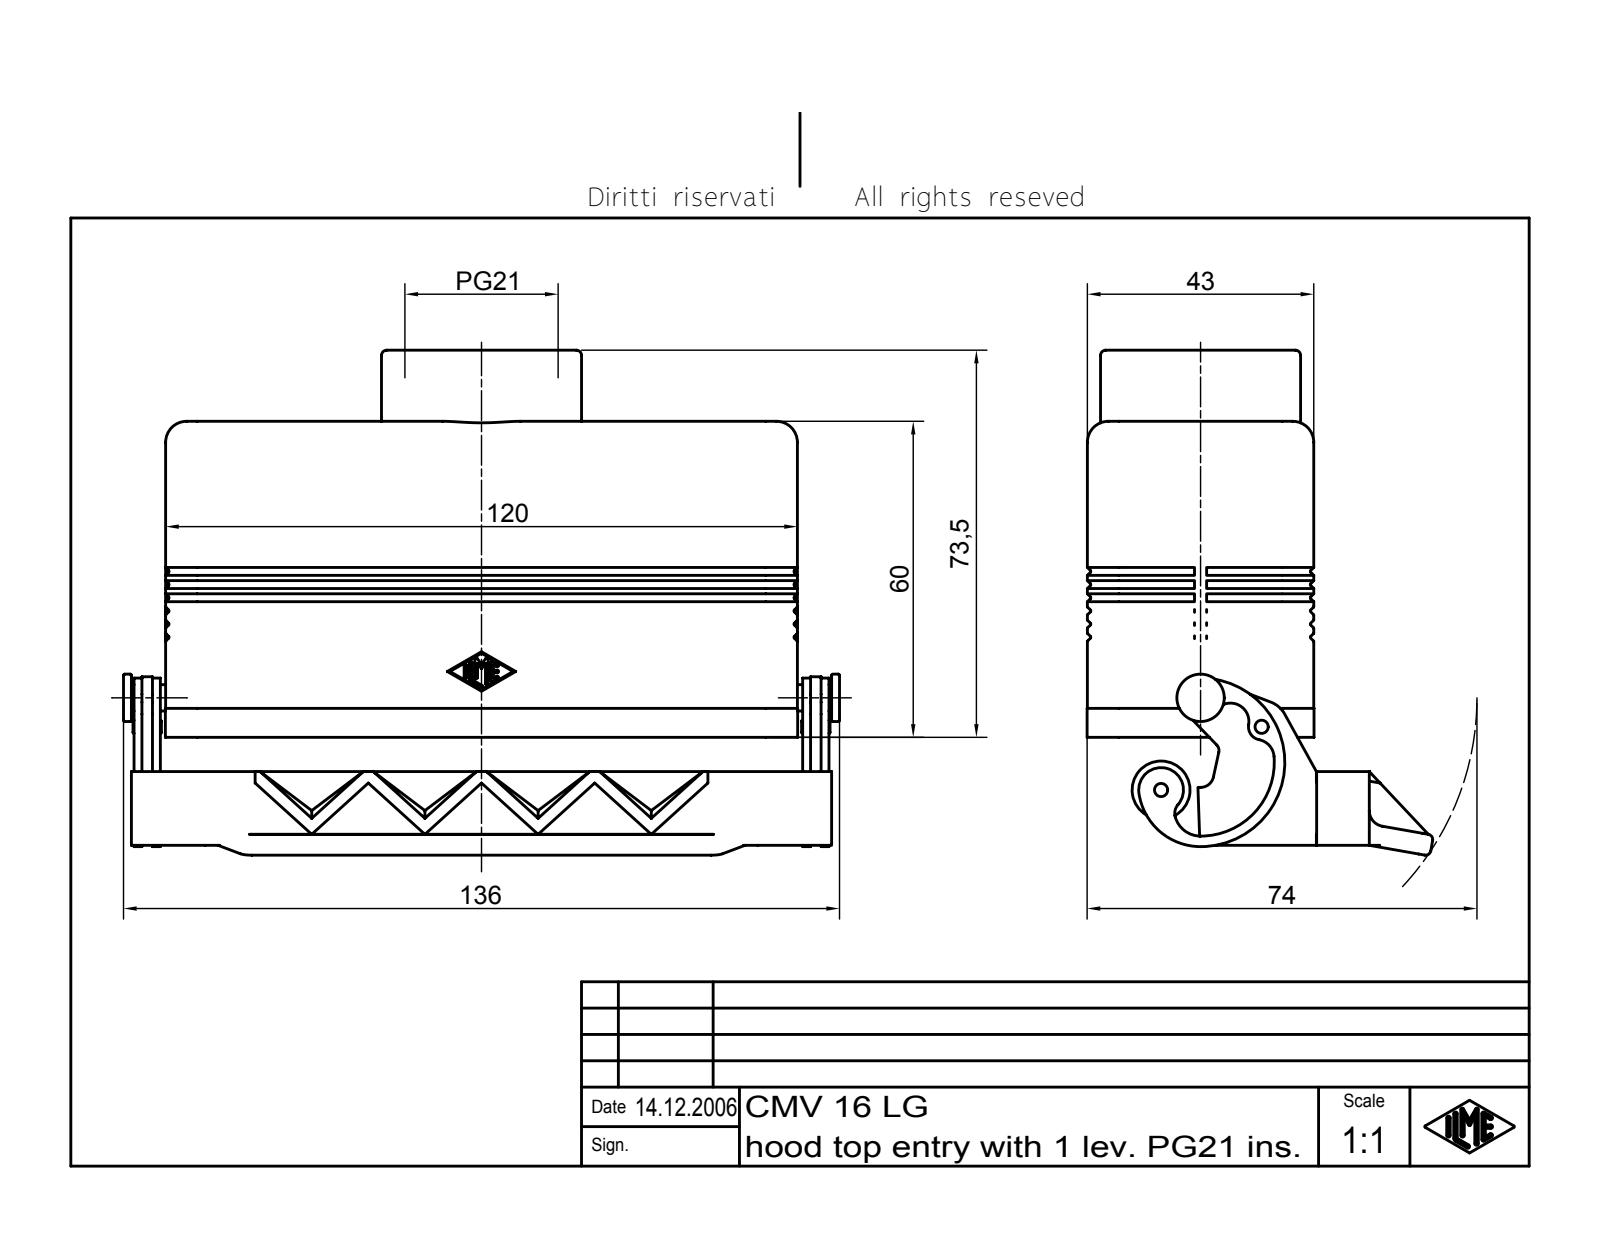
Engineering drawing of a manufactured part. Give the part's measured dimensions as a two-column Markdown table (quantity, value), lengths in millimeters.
| quantity | value |
| --- | --- |
| part name | CMV 16 LG |
| STEP written by | Autodesk Inventor 7 (AUTOMOTIVE_DESIGN) |
| units | millimeters |
| bodies | 1 solid, 925 faces (216 planar, 308 cylindrical, 401 other) |
| overall size | 136 × 95.87 × 65.64 |
| volume | 113 735 mm³ |
| surface area | 62 209 mm² |
| round holes (diameter × count) | 2.5 × 1, 24.78 × 1, 26.78 × 1 |
| round bosses / shafts (diameter × count) | 38 × 1, 11 × 1, 9 × 1, 5 × 1, 3.1 × 1, 2 × 1 |
| partial cylindrical surfaces (radius × count) | 0.2 × 52, 0.25 × 32, 2.5 × 9, 1 × 6, 4 × 5, 2.45 × 4, 6 × 4, 6.05 × 4 |
| main face-to-face distances | 3.5, 39.5, 36, 43, 3.55, 116.5, 3.6, 4.5, 120, 39.55 |
